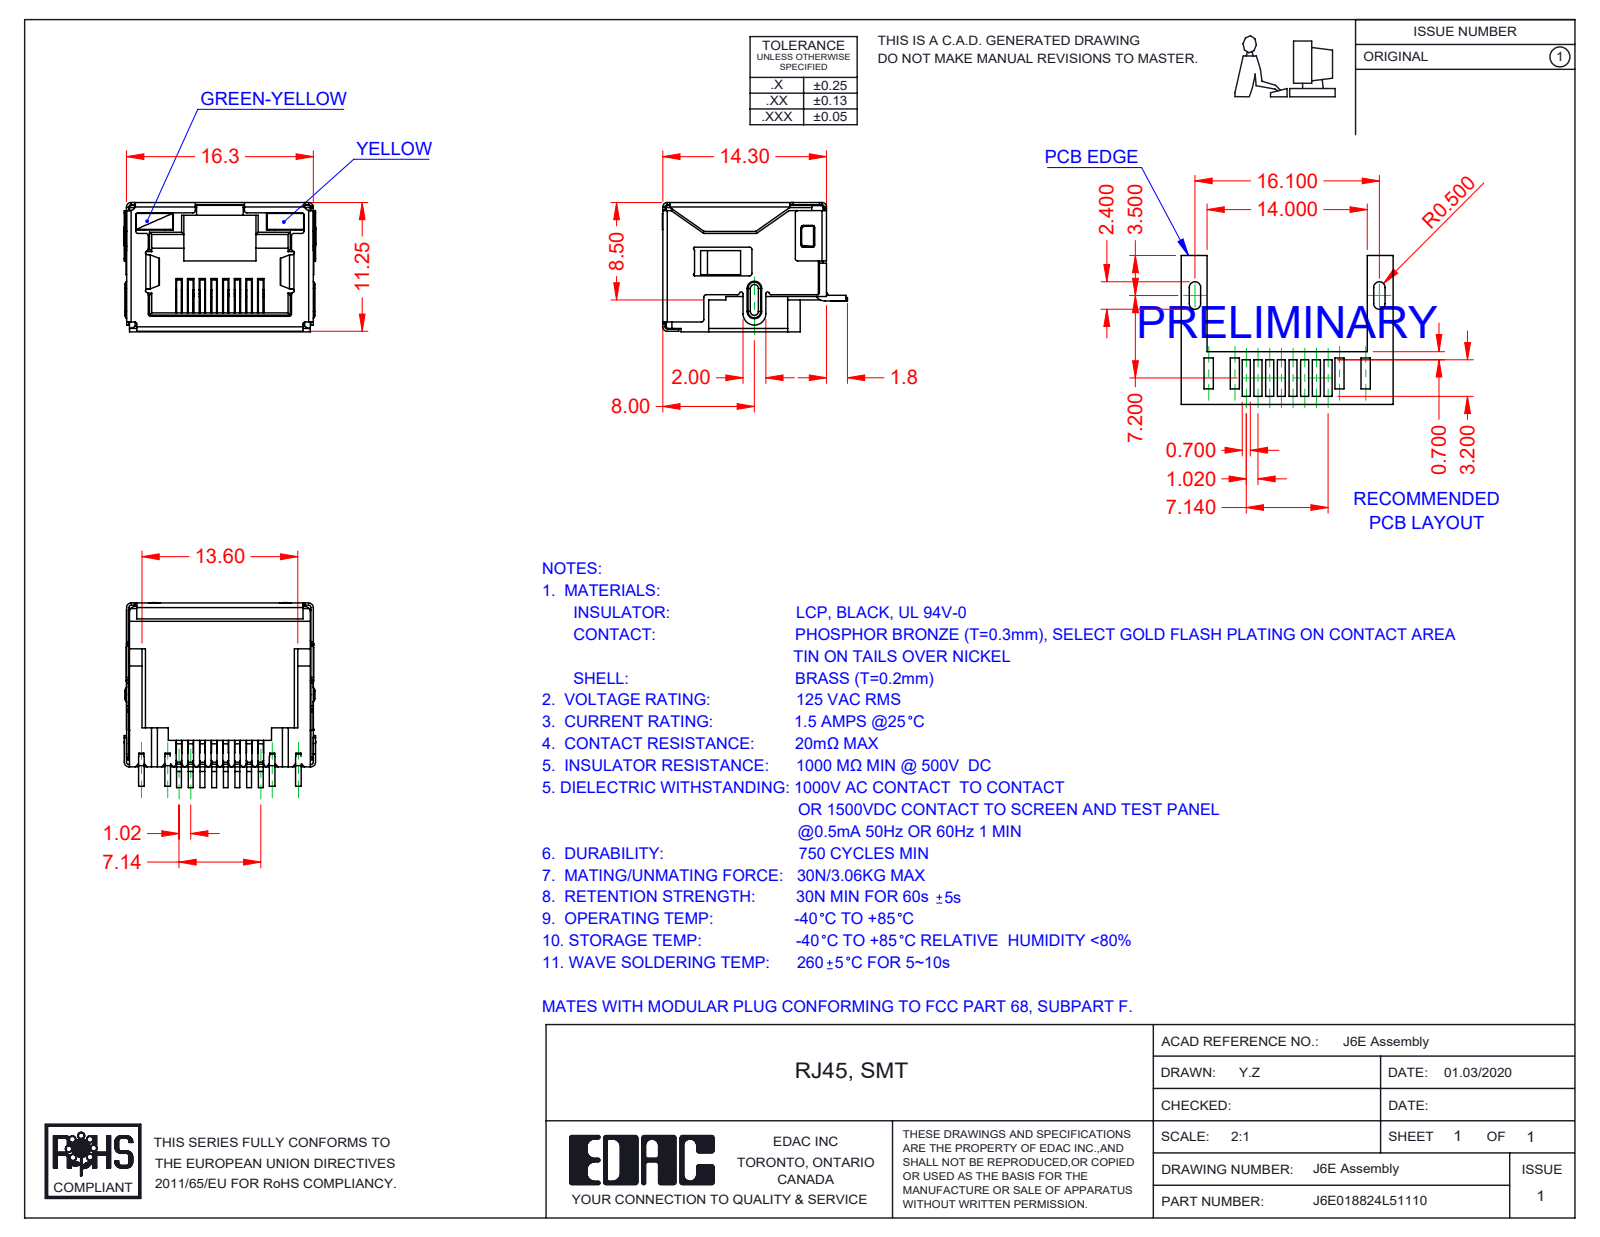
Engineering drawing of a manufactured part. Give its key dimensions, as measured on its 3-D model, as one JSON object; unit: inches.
{"part_name": "6E Insulator_LED; 6E LED RH_1-Yellow; 6E LED LH_5-Green-Yellow; 6E Shield_LED (+2 more)", "step_written_by": "SolidWorks 2016 (CONFIG_CONTROL_DESIGN)", "units": "inches", "bodies": {"solids": 12, "faces": 1498, "planar": 1099, "cylindrical": 349, "other": 50}, "overall_size": [0.659, 0.636, 0.445], "volume_in3": 0.068, "surface_area_in2": 6.27, "partial_cylinders_radius": [[0.008, 82], [0.01, 17], [0.016, 13], [0.02, 13], [0.004, 10], [0.006, 7], [0.012, 4], [0.039, 3]], "face_to_face_distances": [0.435, 0.632, 0.634, 0.624, 0.437, 0.445, 0.094, 0.028, 0.388, 0.019]}
